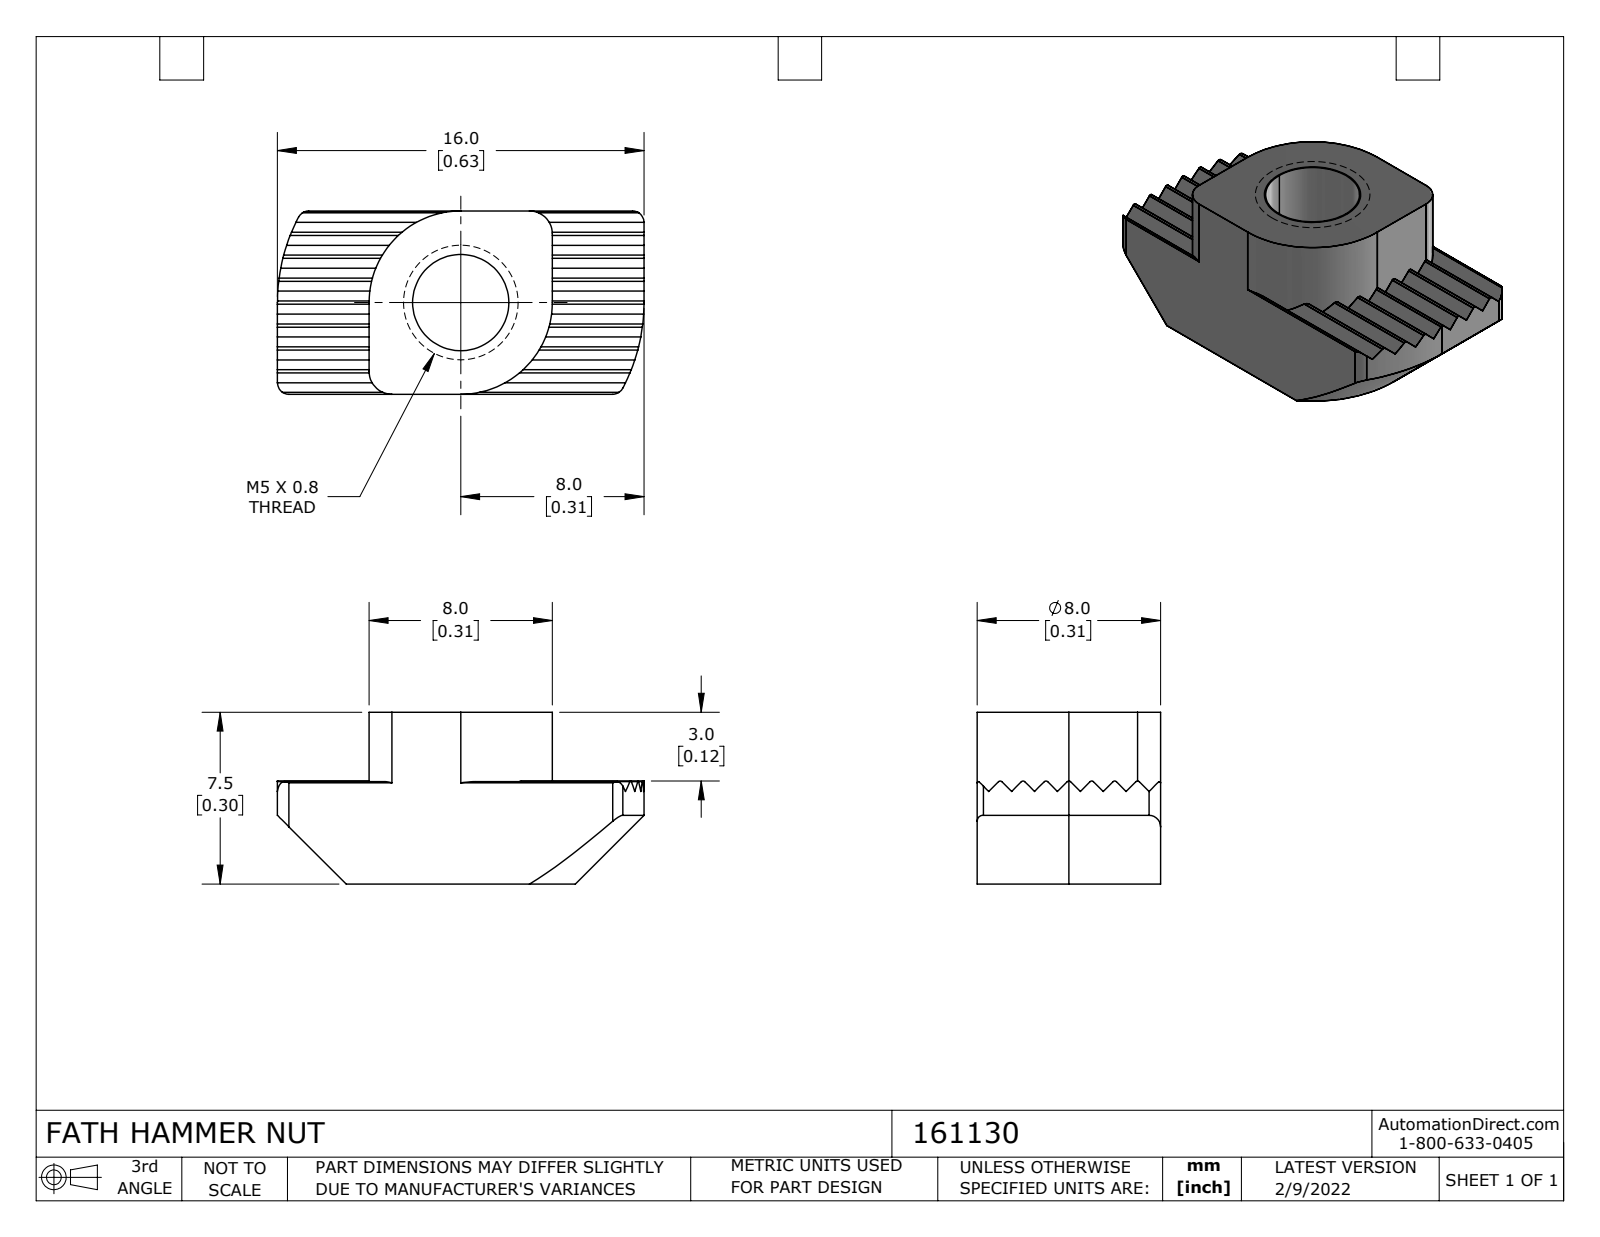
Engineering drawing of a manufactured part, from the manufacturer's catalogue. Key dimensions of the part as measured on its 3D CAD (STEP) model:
Part name (STEP PRODUCT): 161130
STEP written by: SolidWorks 2021 (CONFIG_CONTROL_DESIGN)
Units: millimetres
Bodies: 2 solids, 152 faces (84 planar, 64 cylindrical, 4 other)
Overall size (bounding box): 16 × 8 × 7.5
Volume: 1 086 mm³ · Surface area: 1 174 mm²
Round holes (diameter × count): ⌀4.1 ×1, ⌀4.2 ×1
Partial cylindrical surfaces — rounded edges, fillets, slot ends (radius × count): R0.1 ×7, R0.5 ×4, R1 ×2, R4 ×1, R8 ×1
Main face-to-face distances: 8, 0.71, 2.12, 7.5, 1.41, 2.83, 4.24, 3.53, 1.42, 0.7
